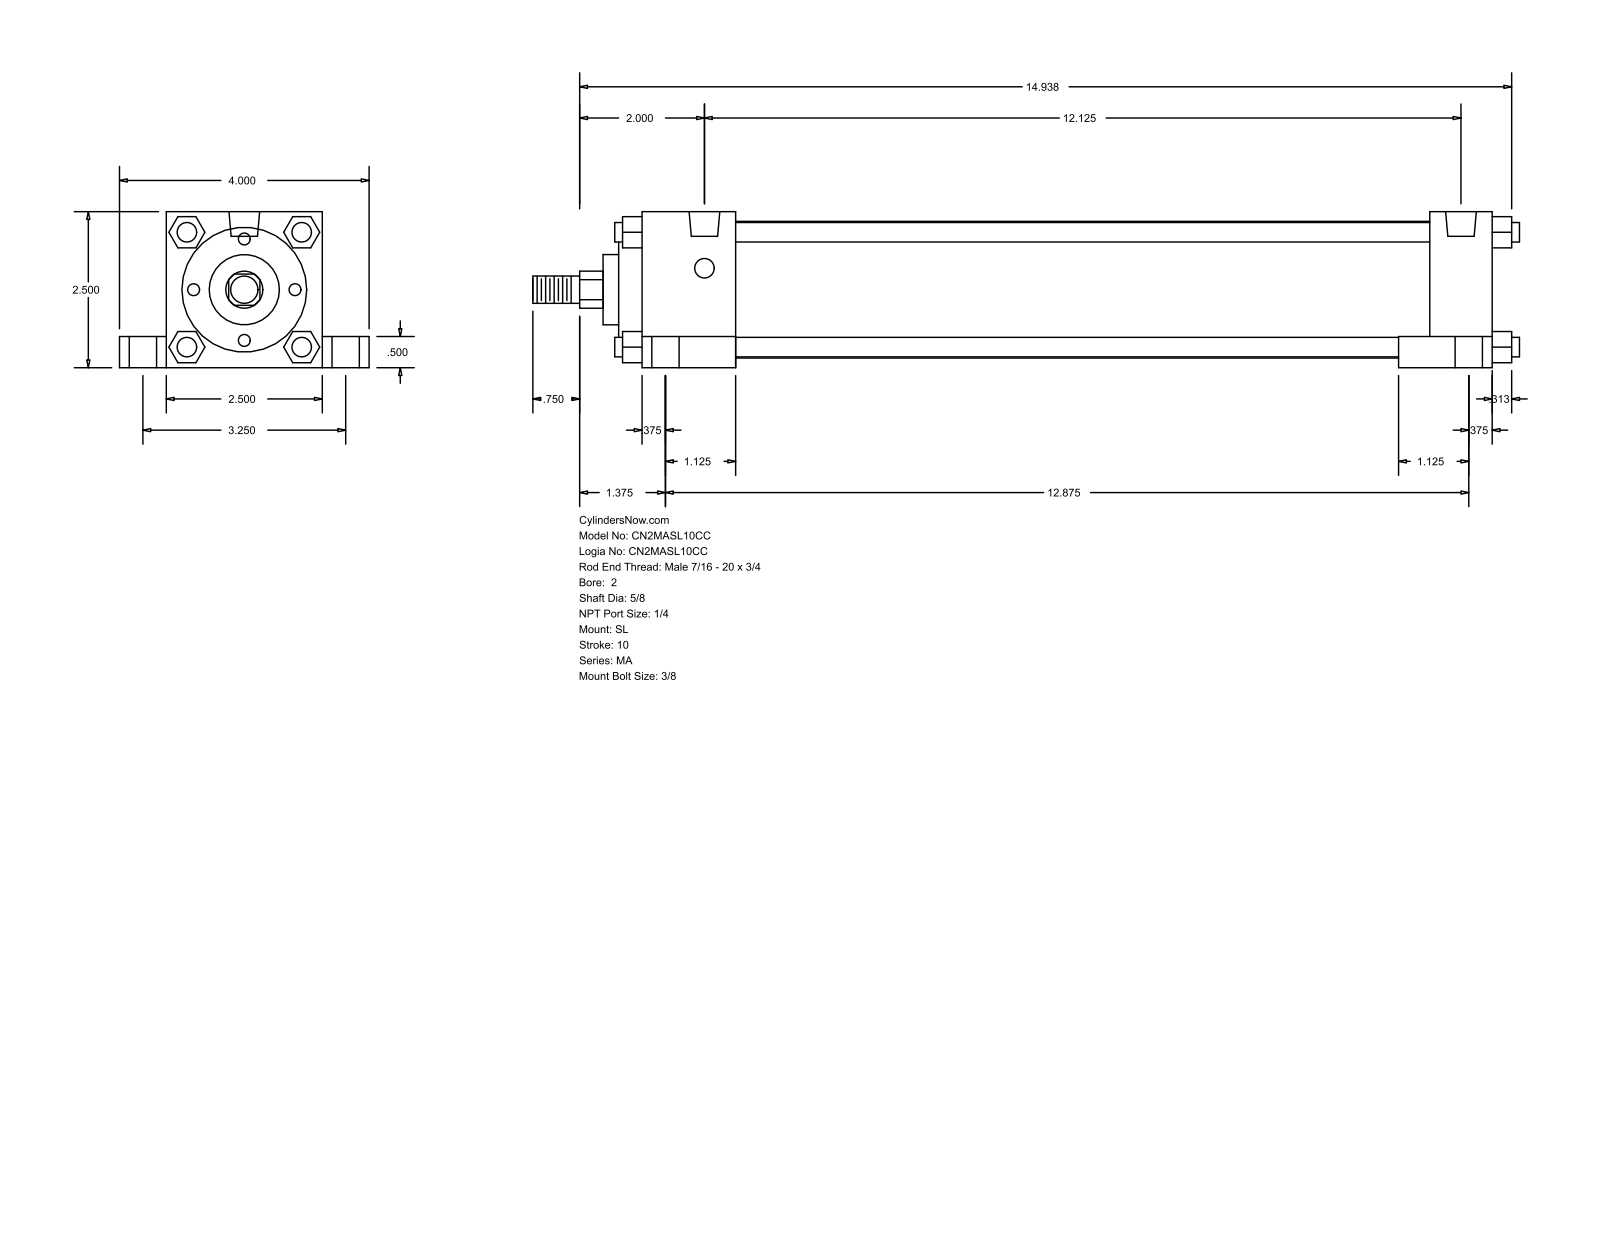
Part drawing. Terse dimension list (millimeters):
name: MA_SL__0200_0.625
written by: GSSL Pune (CONFIG_CONTROL_DESIGN)
unit: mm
bodies: 0 solids, 150 faces (113 planar, 37 cylindrical, 0 other)
size: 401.64 × 101.6 × 63.5
holes: 4× ⌀7.94, 4× ⌀11.11, 4× ⌀17.46, 2× ⌀12.49
bosses: 4× ⌀7.94, 1× ⌀55.63, 1× ⌀50.8, 1× ⌀28.57, 1× ⌀15.88, 1× ⌀11.11
rounds: 1× R7.54
face distances: 63.5, 12.7, 9.52, 282.57, 19.05, 82.55, 38.1, 50.8, 346.08, 307.98
hole spacings: 41.39, 44.22, 82.54, 307.97, 313.88, 326.47, 327.03, 337.29
